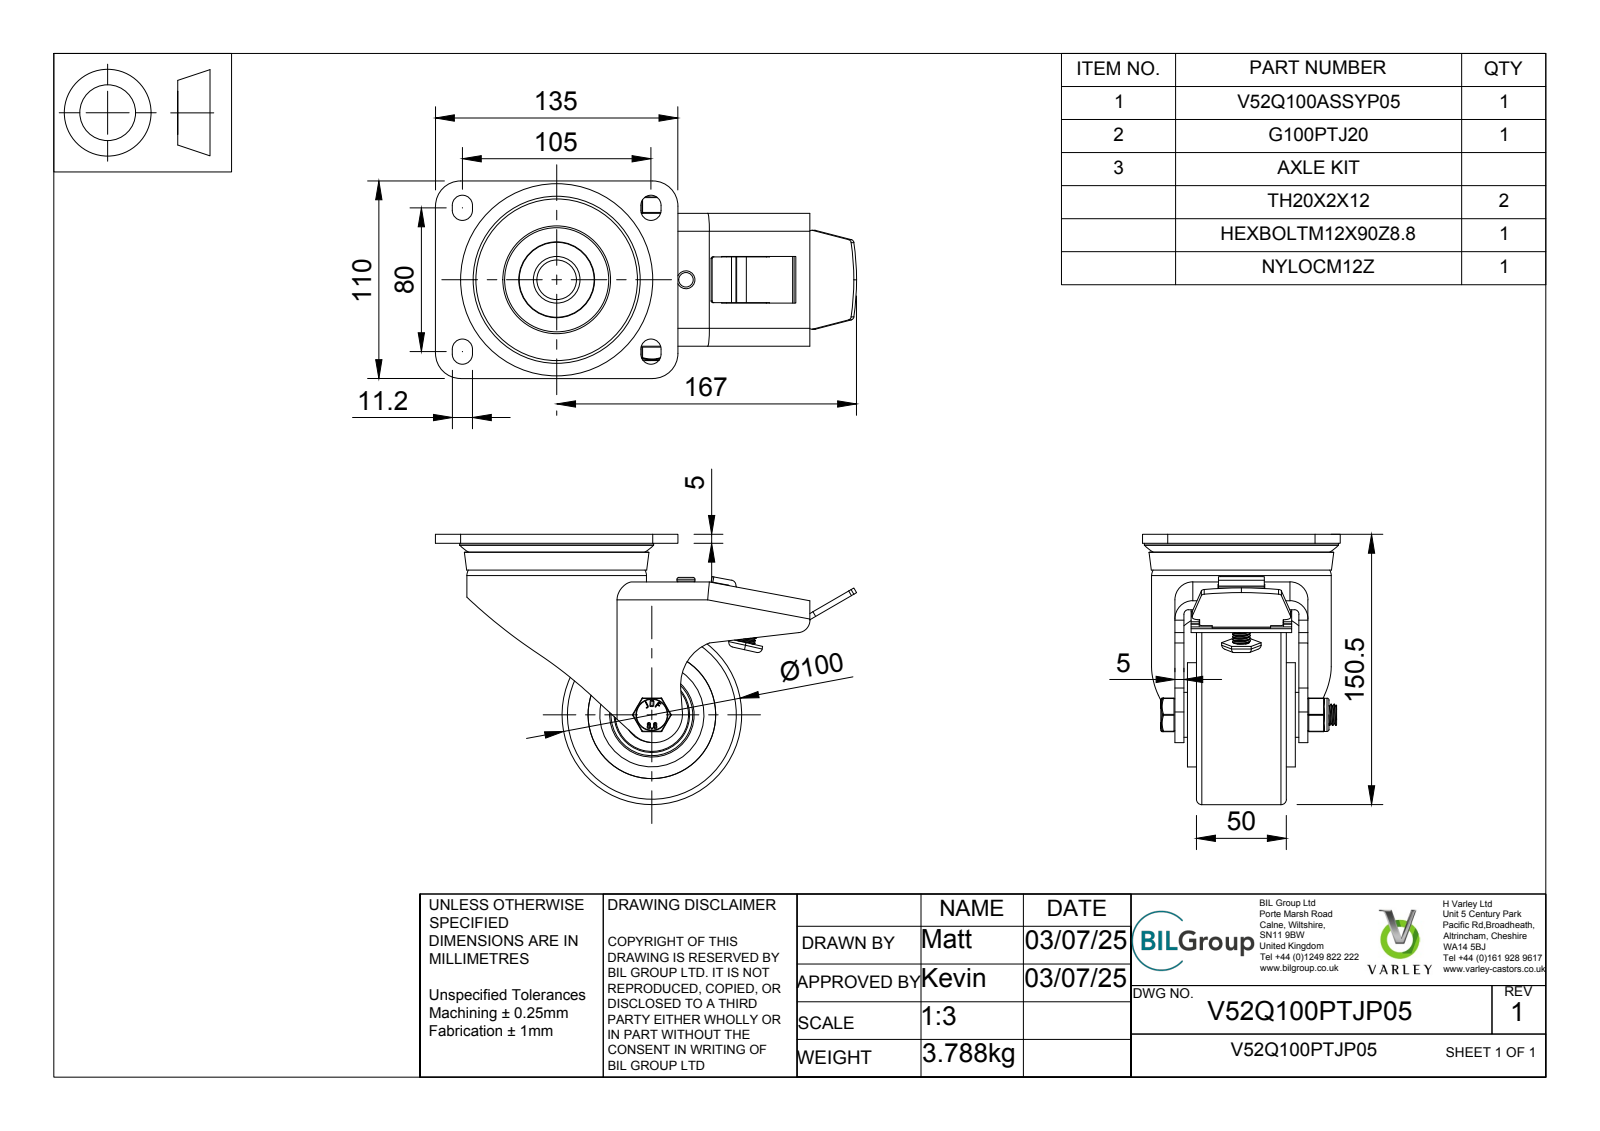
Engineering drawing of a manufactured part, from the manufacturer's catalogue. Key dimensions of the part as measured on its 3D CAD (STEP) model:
Part name (STEP PRODUCT): V52Q100PTJP05 v4; V52Q100ASSYP05 - 64 v1; TOP PLATE; bolt (+5 more)
STEP written by: Autodesk Translation Framework v14.10.0.0 (AUTOMOTIVE_DESIGN)
Units: millimetres
Bodies: 64 solids, 1306 faces (584 planar, 314 cylindrical, 408 other)
Overall size (bounding box): 234.5 × 150.5 × 110
Volume: 656 434 mm³ · Surface area: 256 293 mm²
Round holes (diameter × count): ⌀12 ×2, ⌀6 ×1, ⌀10 ×1, ⌀12.2 ×1, ⌀14 ×1, ⌀20 ×1, ⌀21 ×1, ⌀28.5 ×1, ⌀30.8 ×1, ⌀40.3 ×1, ⌀40.5 ×1, ⌀42 ×1
Round bosses / shafts (diameter × count): ⌀100 ×2, ⌀108 ×1, ⌀81 ×1, ⌀65 ×1, ⌀58 ×1, ⌀40.8 ×1, ⌀31.3 ×1, ⌀27 ×1
Partial cylindrical surfaces — rounded edges, fillets, slot ends (radius × count): R1 ×34, R0.5 ×21, R2.5 ×10, R5.6 ×8, R2 ×7, R0.47 ×4, R0.9 ×4, R10 ×4
Main face-to-face distances: 5, 7, 62, 12, 57, 69, 26.5, 3, 64, 50
Hole centre spacings: 72
